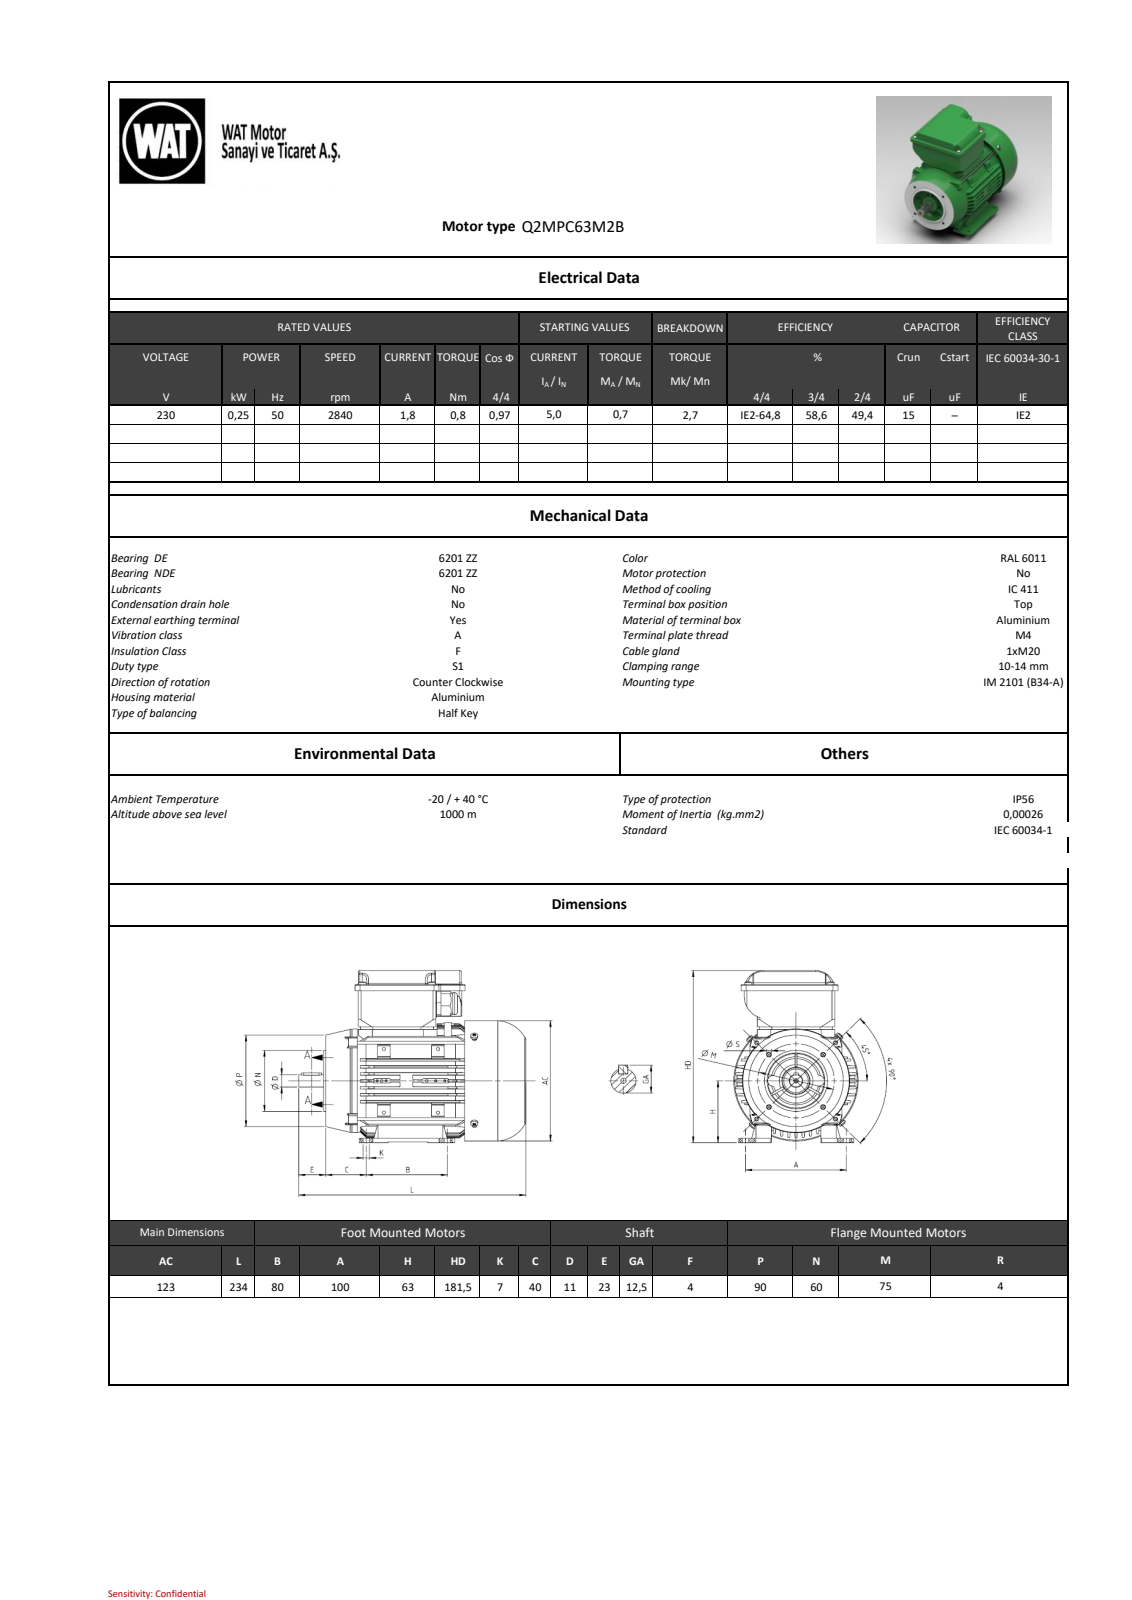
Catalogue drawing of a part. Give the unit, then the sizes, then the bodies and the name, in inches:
Units: inches
Overall size (bounding box): 9.192 × 7.146 × 4.843
Round holes (diameter × count): ⌀0.144 ×10, ⌀0.13 ×9, ⌀0.177 ×8, ⌀0.098 ×6, ⌀0.15 ×4, ⌀0.157 ×4, ⌀0.165 ×4, ⌀0.183 ×4, ⌀0.189 ×4, ⌀0.118 ×3, ⌀0.276 ×2, ⌀0.197 ×1
Round bosses / shafts (diameter × count): ⌀0.315 ×8, ⌀0.157 ×8, ⌀0.118 ×8, ⌀0.189 ×4, ⌀4.843 ×1, ⌀4.764 ×1, ⌀3.898 ×1, ⌀2.362 ×1
Partial cylindrical surfaces — rounded edges, fillets, slot ends (radius × count): R0.02 ×212, R0.039 ×111, R0.079 ×52, R0.197 ×26, R0.098 ×20, R0.157 ×11, R0.118 ×9, R0.217 ×9
Main face-to-face distances: 0.118, 0.059, 0.177, 0.039, 0.276, 1.101, 0.157, 5.807, 7.146, 1.104
Hole centre spacings: 2.165, 2.126, 2.608, 0.024, 1.476, 2.472, 2.48, 2.603
Volume: 37.37 in³ · Surface area: 667.1 in²
Bodies: 36 solids, 2243 faces (1139 planar, 781 cylindrical, 323 other)
Part name (STEP PRODUCT): BY6434017xx_004-TK_QM63-80; BY6424130xx_004-TKK_QM63-80; BY6424111xx_004-MOTOR_KAPAGI_QS63FC_ISLEME; BY6423003xx_006-FAN_KAPAGI_QS63 (+8 more)
STEP written by: SIEMENS PLM Software NX2206.8101 (AUTOMOTIVE_DESIGN)
